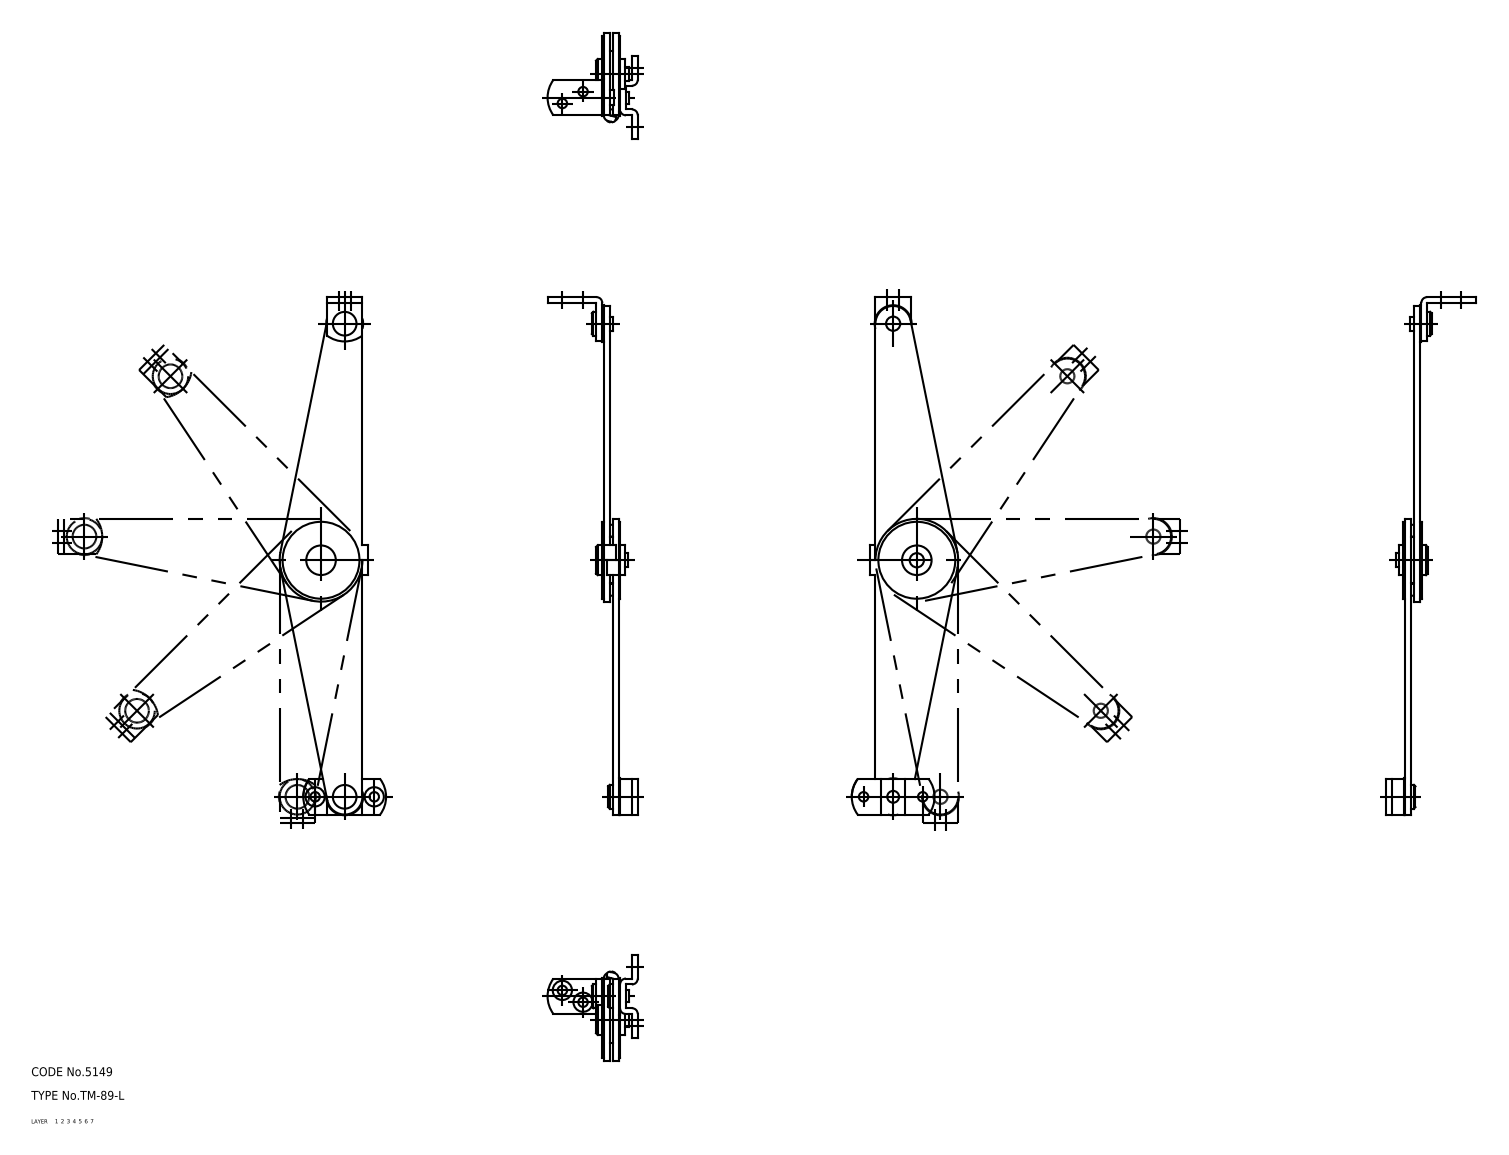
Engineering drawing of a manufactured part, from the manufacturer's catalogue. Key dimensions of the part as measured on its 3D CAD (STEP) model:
Part name (STEP PRODUCT): ball; spring; arm; washer_C (+8 more)
STEP written by: CADfix (AUTOMOTIVE_DESIGN)
Units: millimetres
Bodies: 15 solids, 155 faces (0 planar, 0 cylindrical, 155 other)
Overall size (bounding box): 175.25 × 36 × 30.5
Volume: 10 893 mm³ · Surface area: 14 967 mm²
